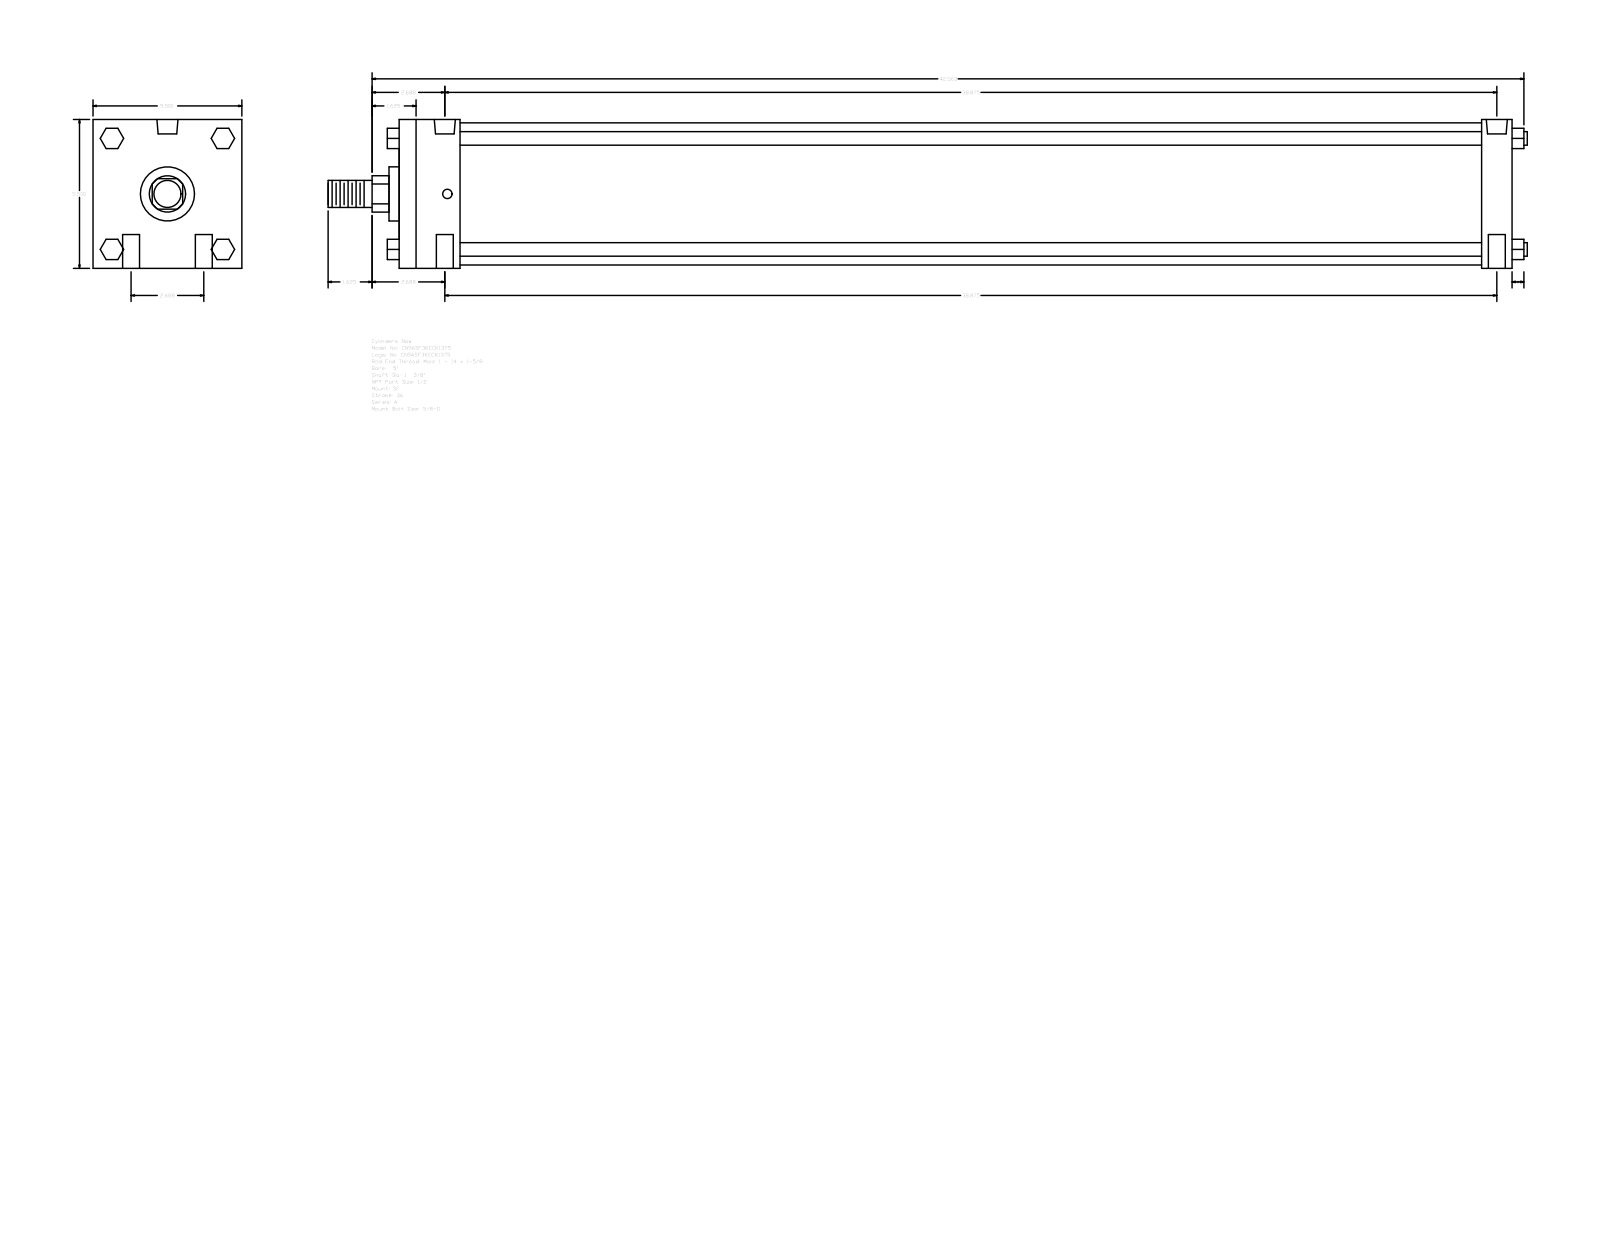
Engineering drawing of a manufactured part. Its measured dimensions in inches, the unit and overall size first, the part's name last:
Units: inches
Overall size (bounding box): 44.313 × 5.5 × 5.5
Round holes (diameter × count): ⌀0.625 ×4, ⌀0.344 ×2, ⌀0.778 ×2
Round bosses / shafts (diameter × count): ⌀0.5 ×4, ⌀5.25 ×1, ⌀2 ×1, ⌀1.375 ×1, ⌀1 ×1
Partial cylindrical surfaces — rounded edges, fillets, slot ends (radius × count): R0.672 ×1
Main face-to-face distances: 5.5, 41.125, 2.25, 40, 37.75, 38.875, 1.125, 0.75, 2.05, 3.55
Hole centre spacings: 1.344, 38.898, 38.875, 2.687, 38.968, 38.687
Bodies: 0 solids, 124 faces (94 planar, 30 cylindrical, 0 other)
Part name (STEP PRODUCT): A_SF__0500_1.375
STEP written by: GSSL Pune (CONFIG_CONTROL_DESIGN)
